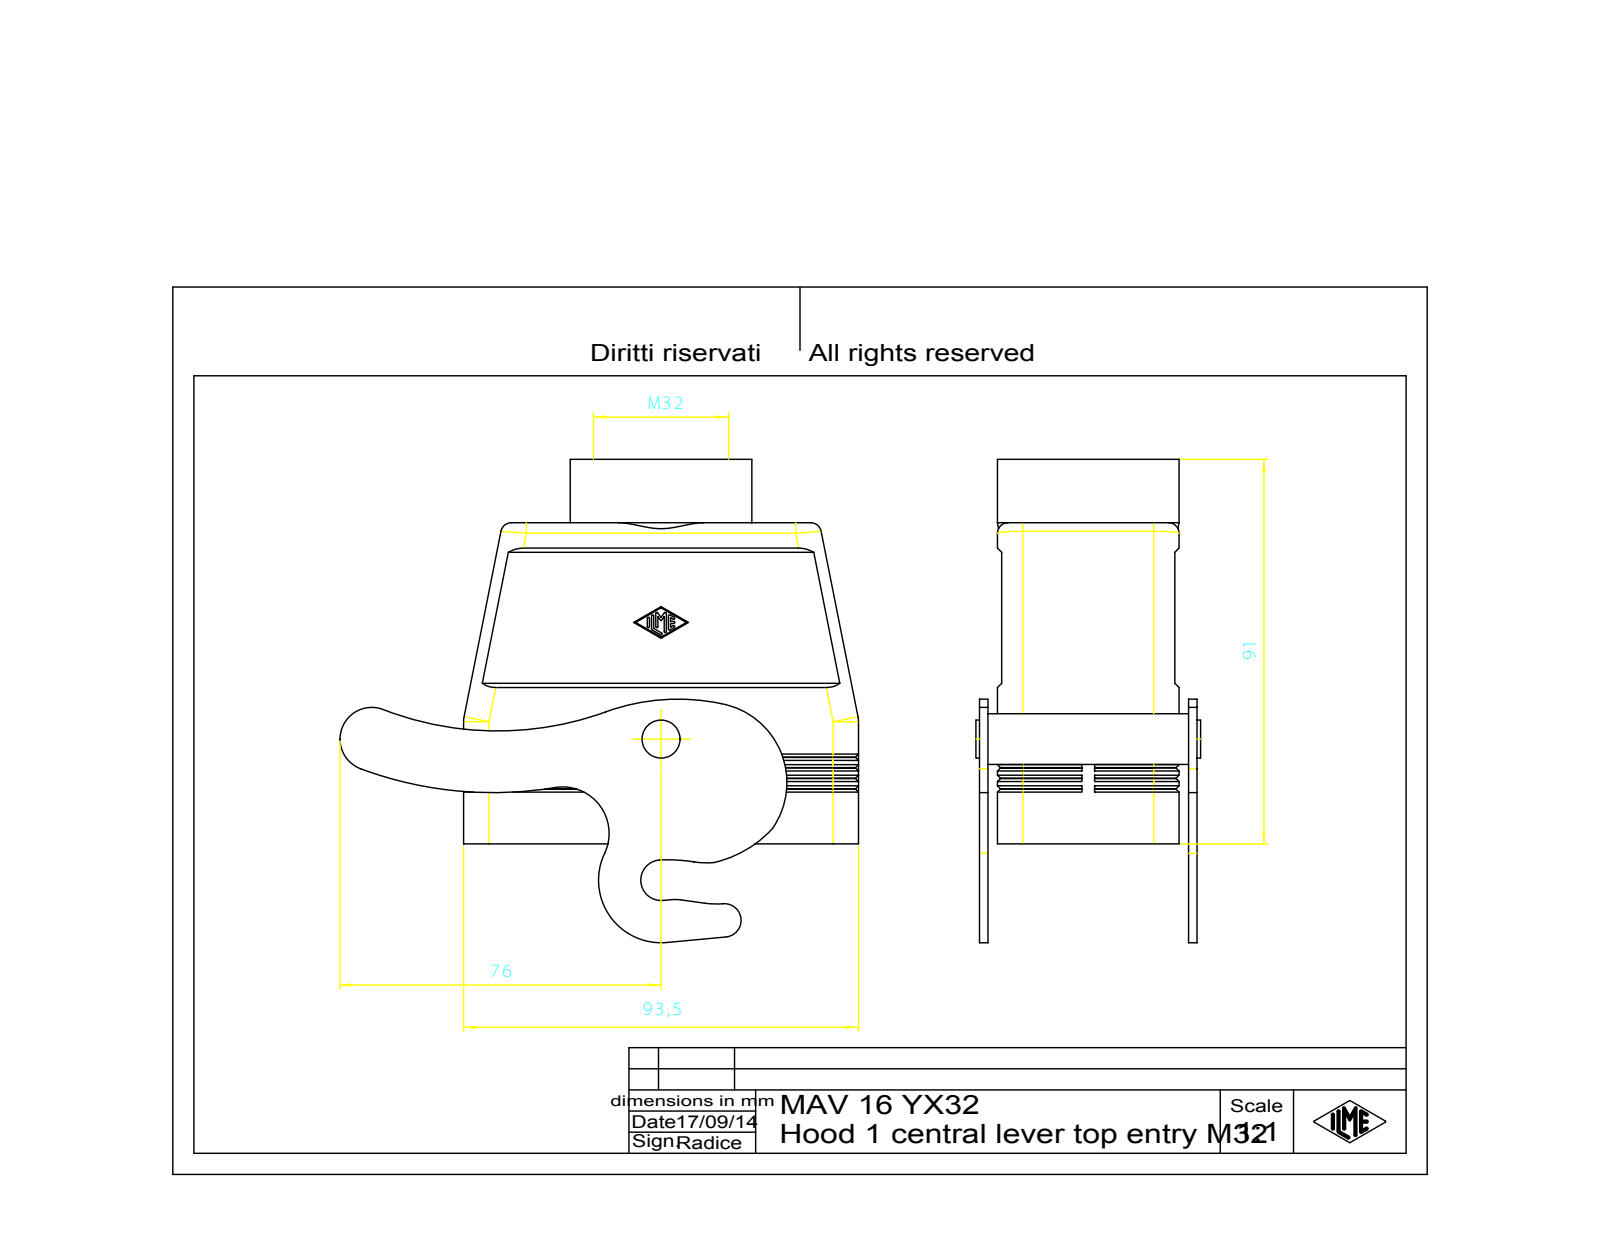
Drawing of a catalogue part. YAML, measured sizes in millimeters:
part_name: "MAV_16_YX32"
step_written_by: "Creo Elements/Direct Modeling 18.0B 02-Dec-2011 (C) Parametric Technology GmbH (AUTOMOTIVE_DESIGN)"
units: millimeters
bodies: {solids: 1, faces: 377, planar: 189, cylindrical: 134, other: 54}
overall_size: [122.75, 114.4, 53.2]
volume: 96637
surface_area: 60501
round_holes:
  - {diameter: 2.46, count: 4}
  - {diameter: 4, count: 4}
  - {diameter: 5, count: 1}
  - {diameter: 30, count: 1}
  - {diameter: 32, count: 1}
round_bosses_or_shafts:
  - {diameter: 43, count: 1}
  - {diameter: 31, count: 1}
  - {diameter: 12, count: 1}
  - {diameter: 9, count: 1}
  - {diameter: 4.8, count: 1}
partial_cylinders:
  - {radius: 0.25, count: 14}
  - {radius: 6, count: 10}
  - {radius: 2, count: 4}
  - {radius: 2.5, count: 4}
  - {radius: 3, count: 4}
  - {radius: 5.3, count: 4}
  - {radius: 3.95, count: 1}
  - {radius: 4.8, count: 1}
face_to_face_distances: [44.25, 2, 5.25, 3, 40, 4.25, 7.25, 47.25, 49.5, 2.25]
hole_center_spacings: [41.03, 27, 77.5, 82.07]
